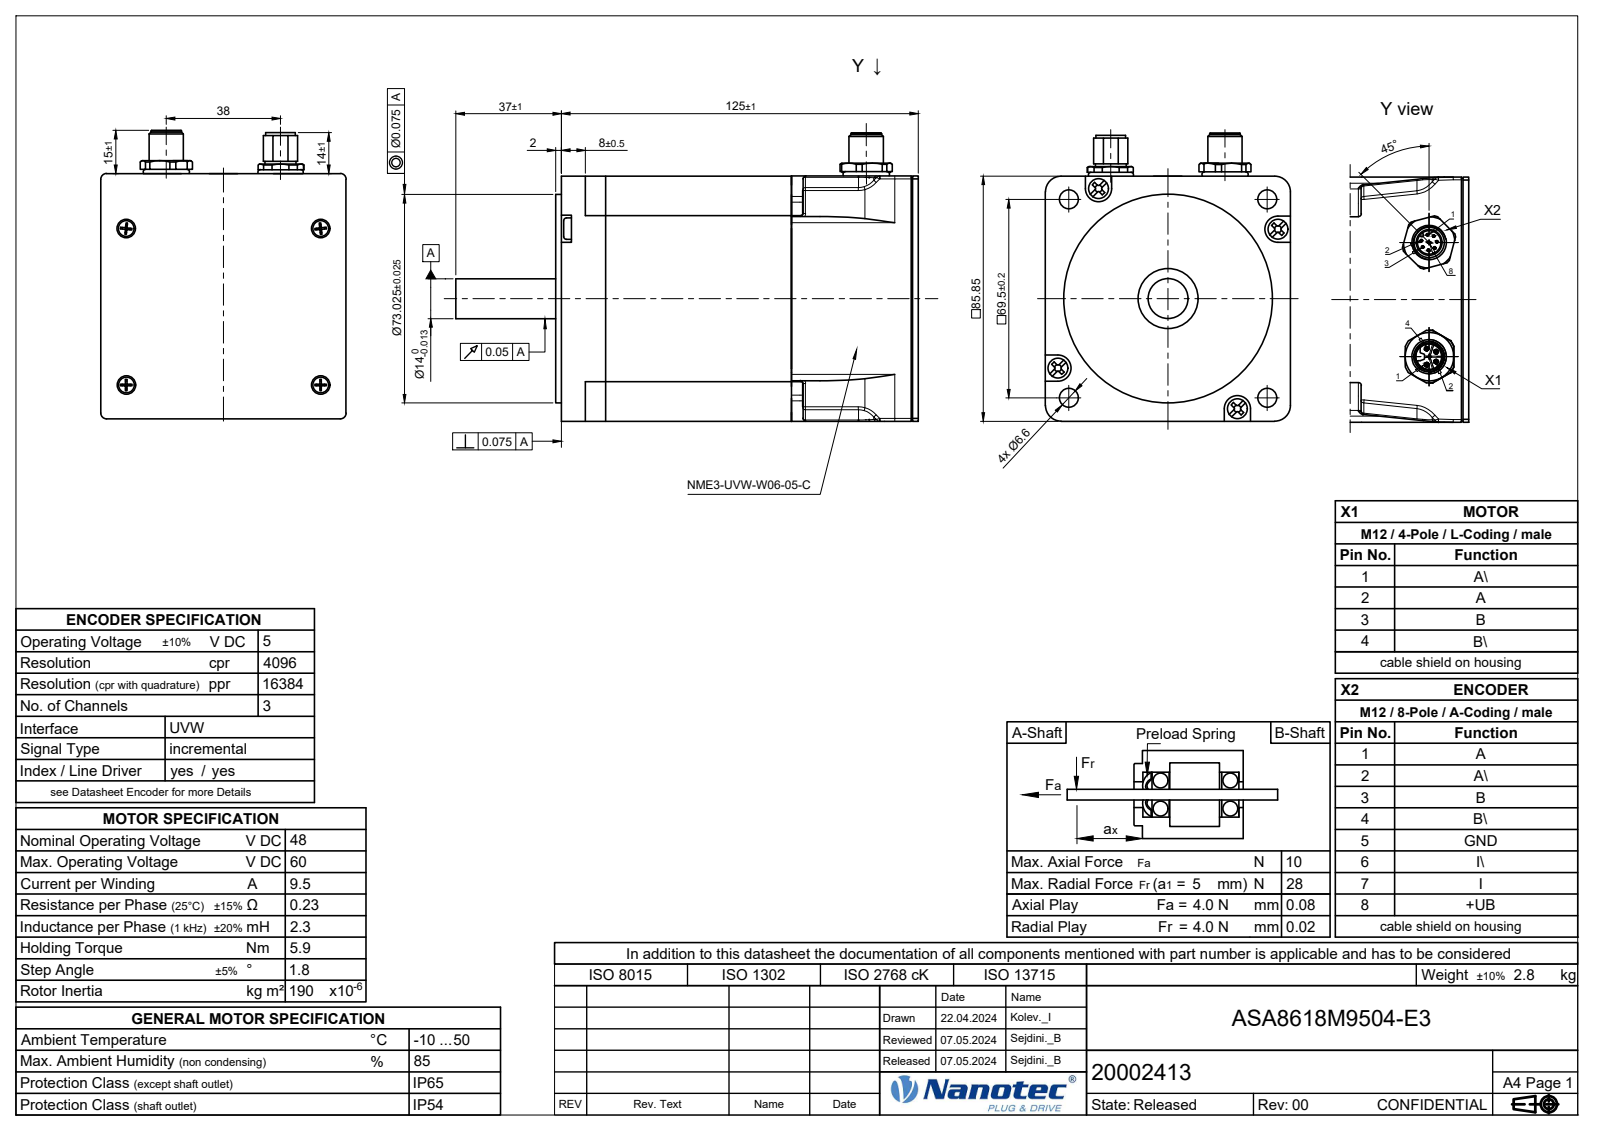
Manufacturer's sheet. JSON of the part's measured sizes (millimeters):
{"part_name": "D-00005795", "step_written_by": "Autodesk Inventor 2021 (AUTOMOTIVE_DESIGN)", "units": "millimeters", "bodies": {"solids": 1, "faces": 663, "planar": 252, "cylindrical": 171, "other": 240}, "overall_size": [162.08, 100.5, 85.9], "volume_mm3": 870455, "surface_area_mm2": 64135, "round_holes": [[1.55, 5], [2.46, 4], [3.24, 4], [3.4, 4], [6.6, 4], [1.5, 1], [1.6, 1], [2.25, 1], [8.3, 1], [8.9, 1], [9.2, 1], [10.1, 1]], "round_bosses_or_shafts": [[1, 8], [2.8, 4], [1.5, 4], [73.03, 1], [14, 1], [13, 1], [12, 1], [10.8, 1]], "partial_cylinders_radius": [[2, 20], [4.6, 20], [1, 16], [0.3, 10], [5.9, 8], [0.2, 6], [5.5, 4], [18, 4]], "face_to_face_distances": [85.85, 85.9, 127, 2, 125, 58.1, 71.97, 13.88, 13.87, 71.98], "hole_center_spacings": [2.94, 3.46, 5.59, 64.42, 69.5, 13.46, 52.83, 55.9]}
